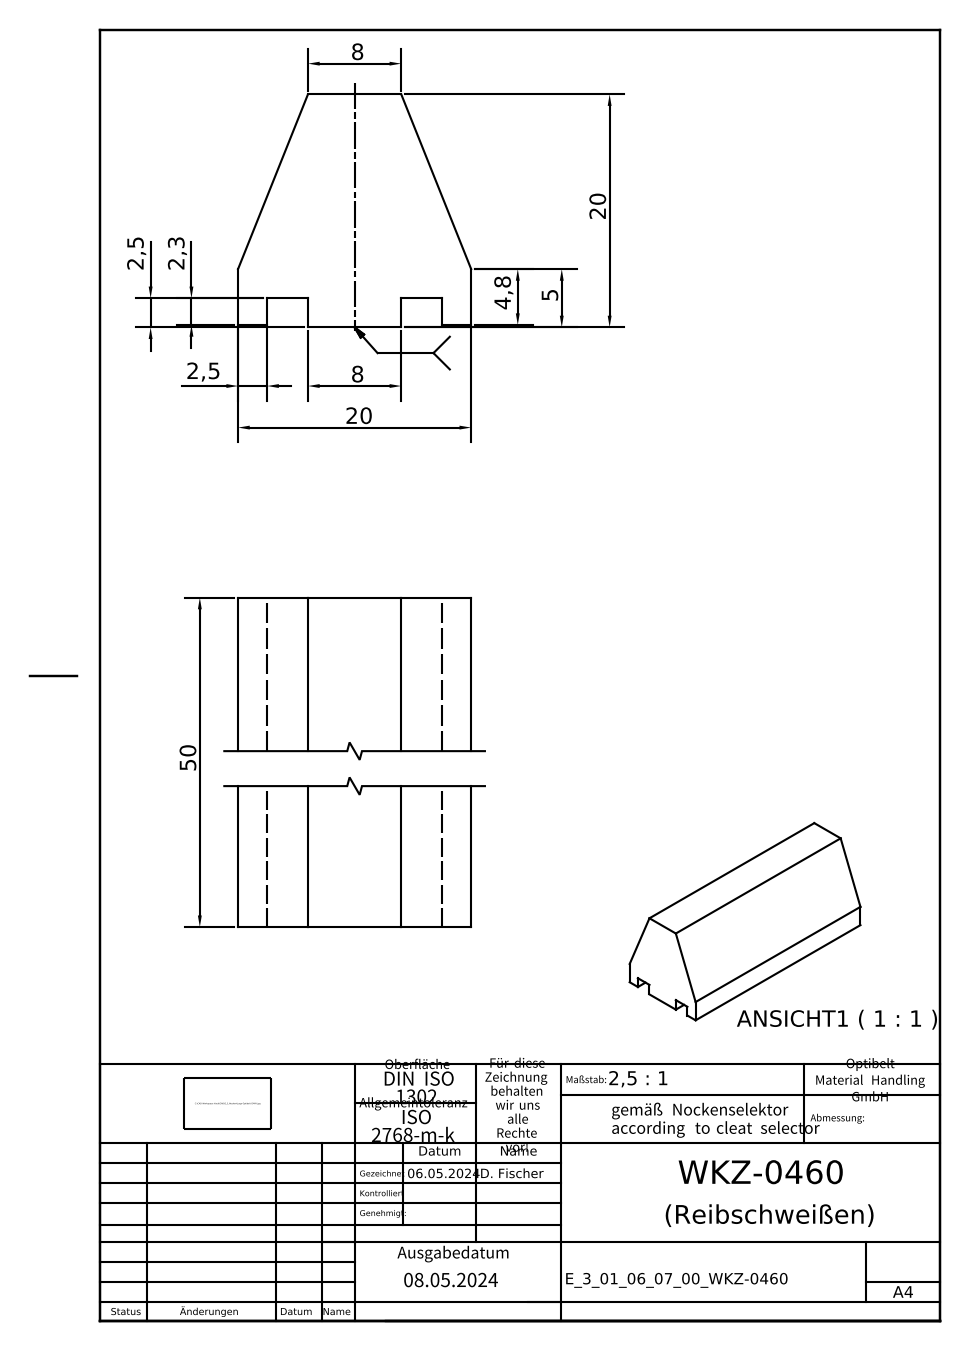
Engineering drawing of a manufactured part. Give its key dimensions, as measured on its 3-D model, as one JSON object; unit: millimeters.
{"part_name": "E_3_01_06_07_00_WKZ-0460", "step_written_by": "Autodesk Inventor 2021 (AUTOMOTIVE_DESIGN)", "units": "millimeters", "bodies": {"solids": 1, "faces": 16, "planar": 16, "cylindrical": 0, "other": 0}, "overall_size": [50, 20, 20], "volume_mm3": 14575, "surface_area_mm2": 4559, "face_to_face_distances": [20, 2.5, 17.5, 50, 2.3, 19.8, 6, 14, 3.5, 11.5]}
